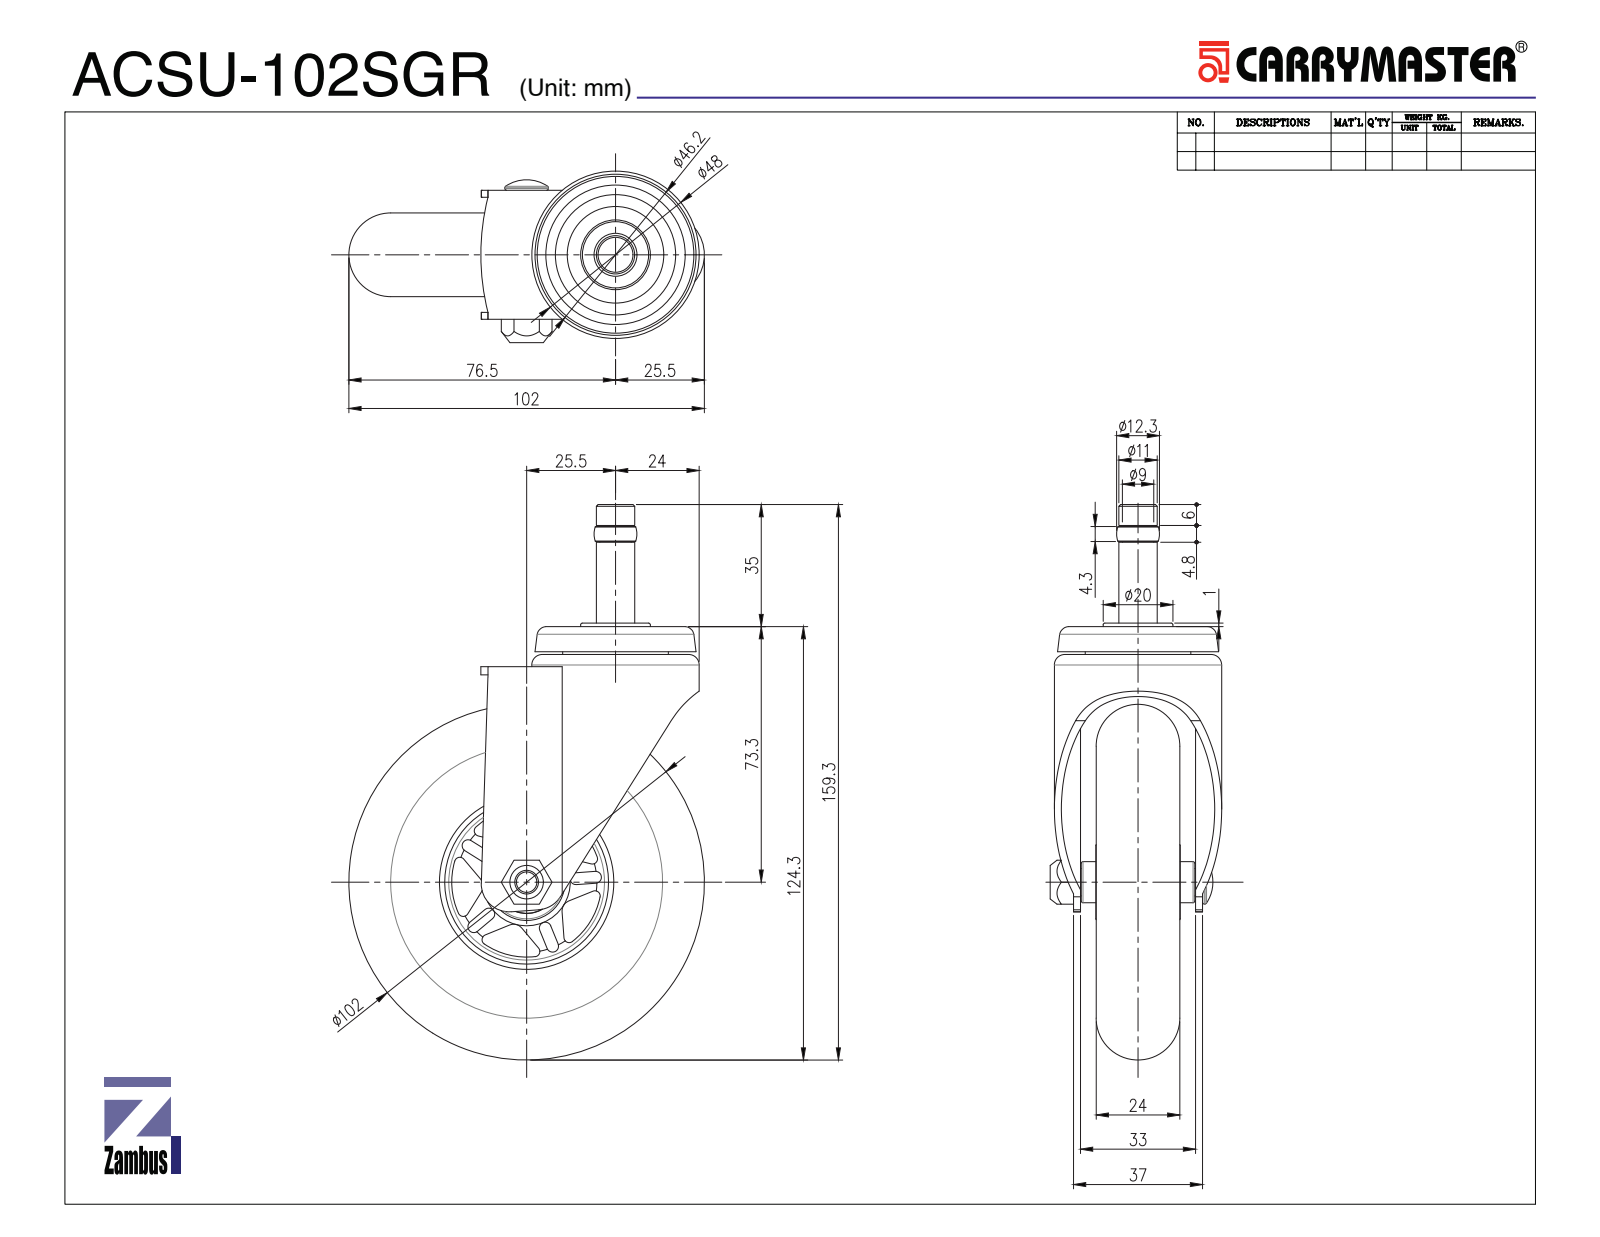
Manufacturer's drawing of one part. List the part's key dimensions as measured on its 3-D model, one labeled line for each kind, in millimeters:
Part name (STEP PRODUCT): ACSU-76 SGR SHAFT; ACSU-76SS FRAME ASSY; ACSU-76 SGR RING; 102RF_102RFACSU-102 WHEEL (+8 more)
STEP written by: SolidWorks 2016 (AUTOMOTIVE_DESIGN)
Units: millimetres
Bodies: 16 solids, 485 faces (137 planar, 200 cylindrical, 148 other)
Overall size (bounding box): 159.3 × 102 × 49.2
Volume: 202 963 mm³ · Surface area: 79 812 mm²
Round holes (diameter × count): ⌀6.8 ×1, ⌀8 ×1, ⌀8.1 ×1, ⌀10 ×1, ⌀11 ×1, ⌀11.9 ×1, ⌀18 ×1, ⌀18.5 ×1, ⌀22 ×1, ⌀26.3 ×1, ⌀39.2 ×1, ⌀44 ×1
Round bosses / shafts (diameter × count): ⌀48 ×1, ⌀42.4 ×1, ⌀30.3 ×1, ⌀20 ×1, ⌀18 ×1, ⌀17.9 ×1, ⌀16 ×1, ⌀12.5 ×1
Partial cylindrical surfaces — rounded edges, fillets, slot ends (radius × count): R1 ×40, R1.5 ×10, R1.7 ×10, R3 ×5, R8 ×2, R21.5 ×1, R29.5 ×1, R30 ×1
Main face-to-face distances: 2, 4.5, 24, 6.5, 30.5, 35, 3.5, 28.5, 37, 8
